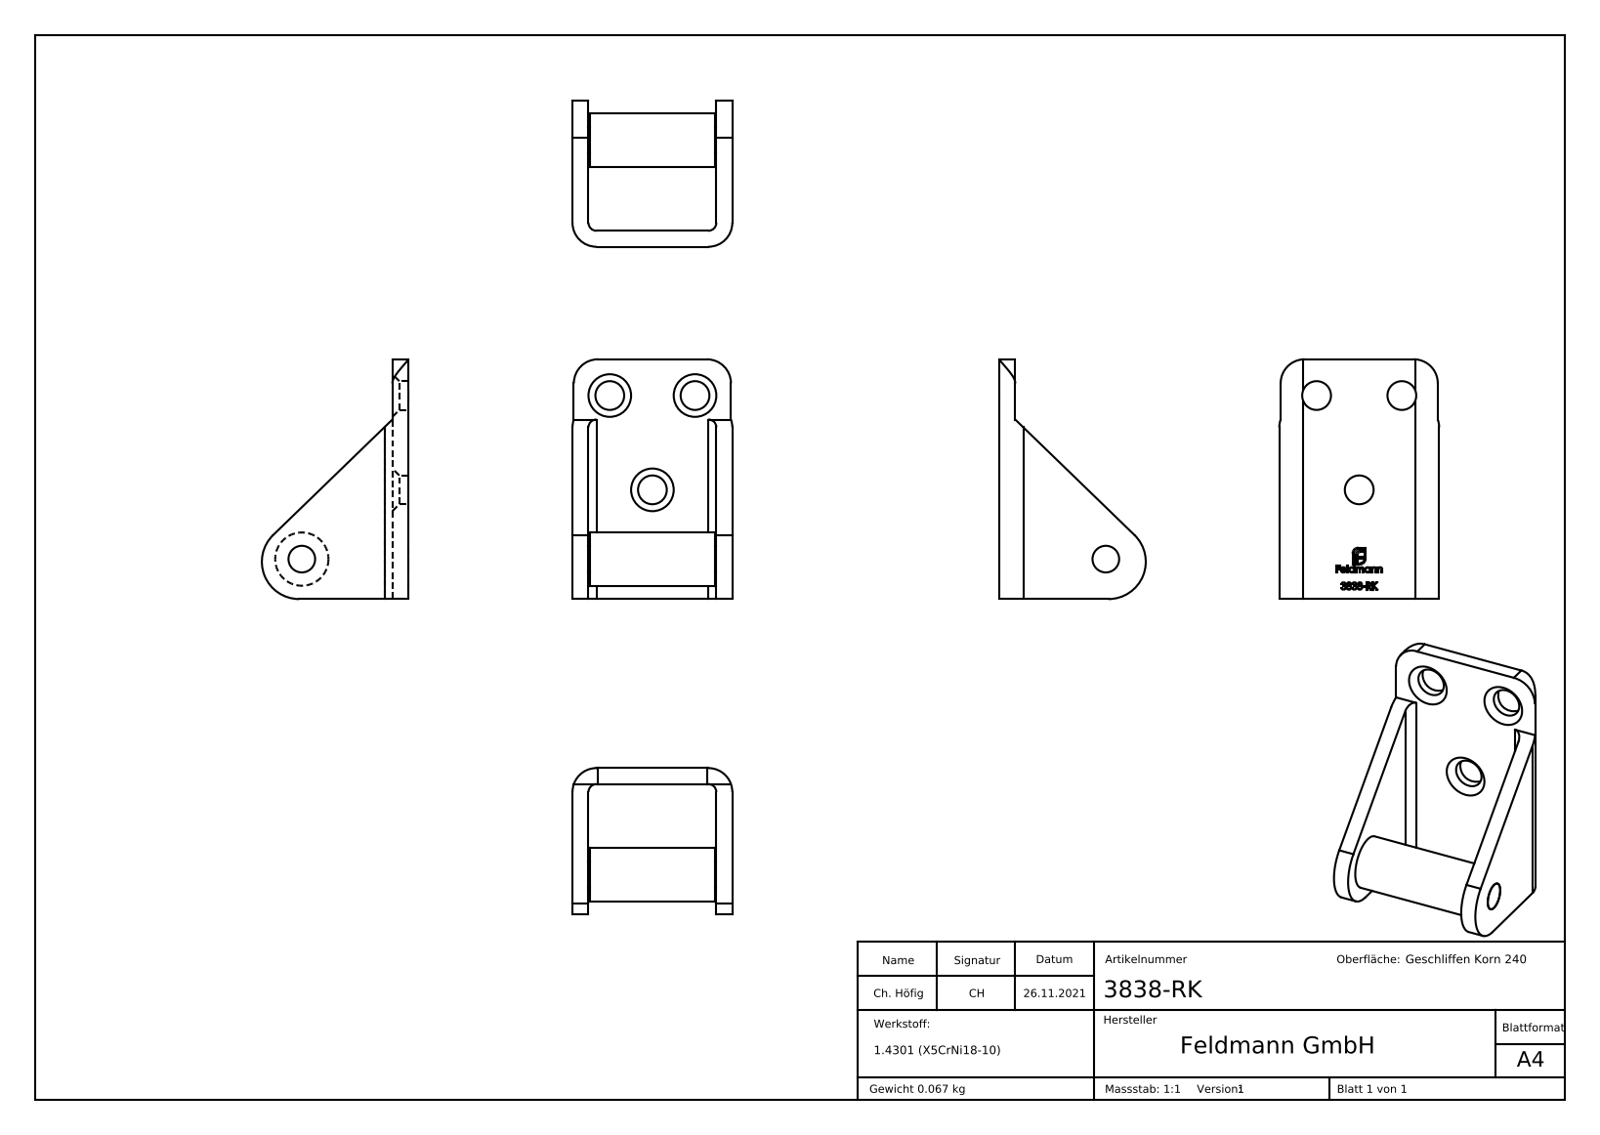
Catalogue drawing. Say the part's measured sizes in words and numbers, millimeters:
The part is named "3838-RK". Its 3-D file was written by "SolidWorks 2018 (CONFIG_CONTROL_DESIGN)". It is 2 solids with 300 faces: 146 planar, 16 cylindrical and 138 other. Overall it measures 45 by 30 by 27.5 millimeters. Its volume is 8 426 cubic millimeters and its surface area 6 184 square millimeters. Round holes: 3 of diameter 5.4, 1 of diameter 5. Round bosses or shafts: 1 of diameter 10. Partial cylindrical surfaces (rounded edges, fillets, slot ends): 4 of radius 4.5, 2 of radius 1.5, 1 of radius 7. The main face-to-face distances are 3, 27, 30, 24, 3.2, 26.8, 23.8, 45, 23.6, 2.9. The hole center spacings are 19.42, 16.
